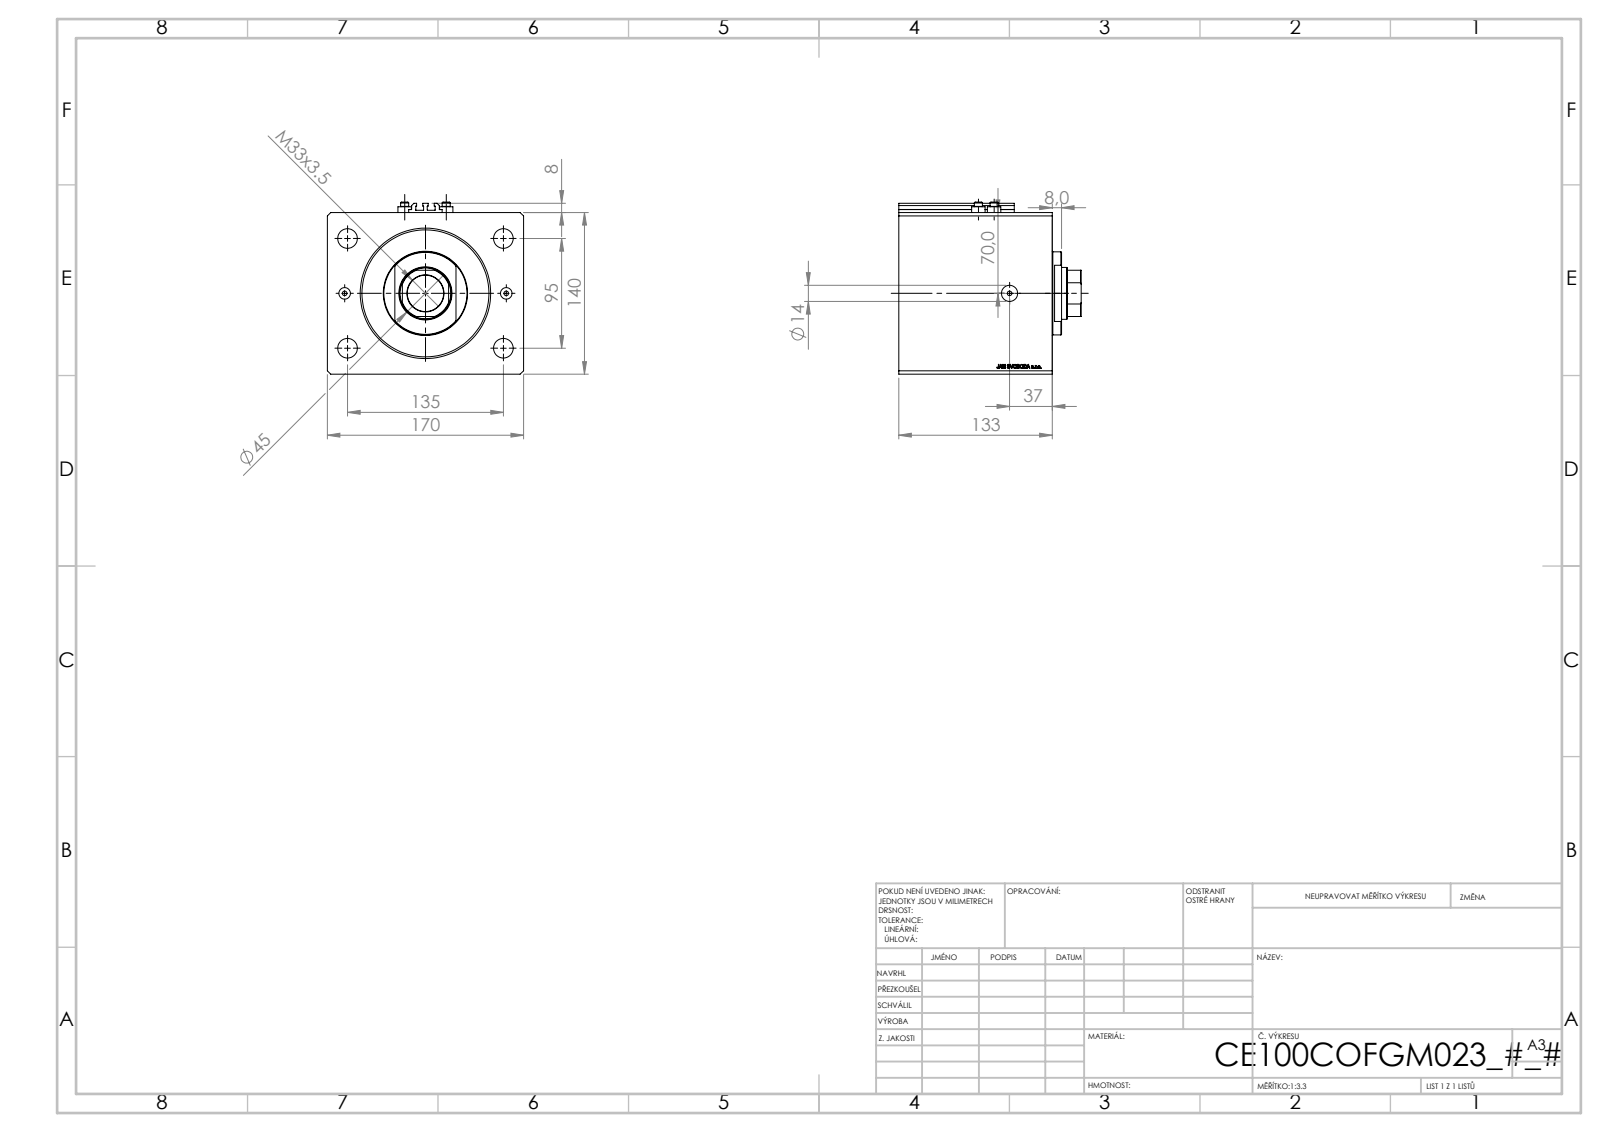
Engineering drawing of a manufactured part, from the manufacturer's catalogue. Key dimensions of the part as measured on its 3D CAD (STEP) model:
Part name (STEP PRODUCT): ALLEN BOLT V250CE; V250CE_C_Body; V250CE_C_VCP; V250CE_VC_C
STEP written by: SolidWorks 2019 (CONFIG_CONTROL_DESIGN)
Units: millimetres
Bodies: 8 solids, 1034 faces (504 planar, 86 cylindrical, 444 other)
Overall size (bounding box): 170 × 158 × 149
Volume: 2 918 000 mm³ · Surface area: 285 232 mm²
Round holes (diameter × count): ⌀4 ×8, ⌀17 ×4, ⌀10 ×2, ⌀14 ×2, ⌀31.5 ×1, ⌀45 ×1, ⌀100 ×1, ⌀113 ×1
Round bosses / shafts (diameter × count): ⌀11.6 ×4, ⌀7 ×4, ⌀72 ×1
Partial cylindrical surfaces — rounded edges, fillets, slot ends (radius × count): R0.2 ×10, R22 ×1
Main face-to-face distances: 140, 133, 170, 28.9, 104.1, 25, 108, 79.1, 23, 85
Hole centre spacings: 47.57, 82.54, 145.47, 13.6, 36, 38.48, 70, 95
